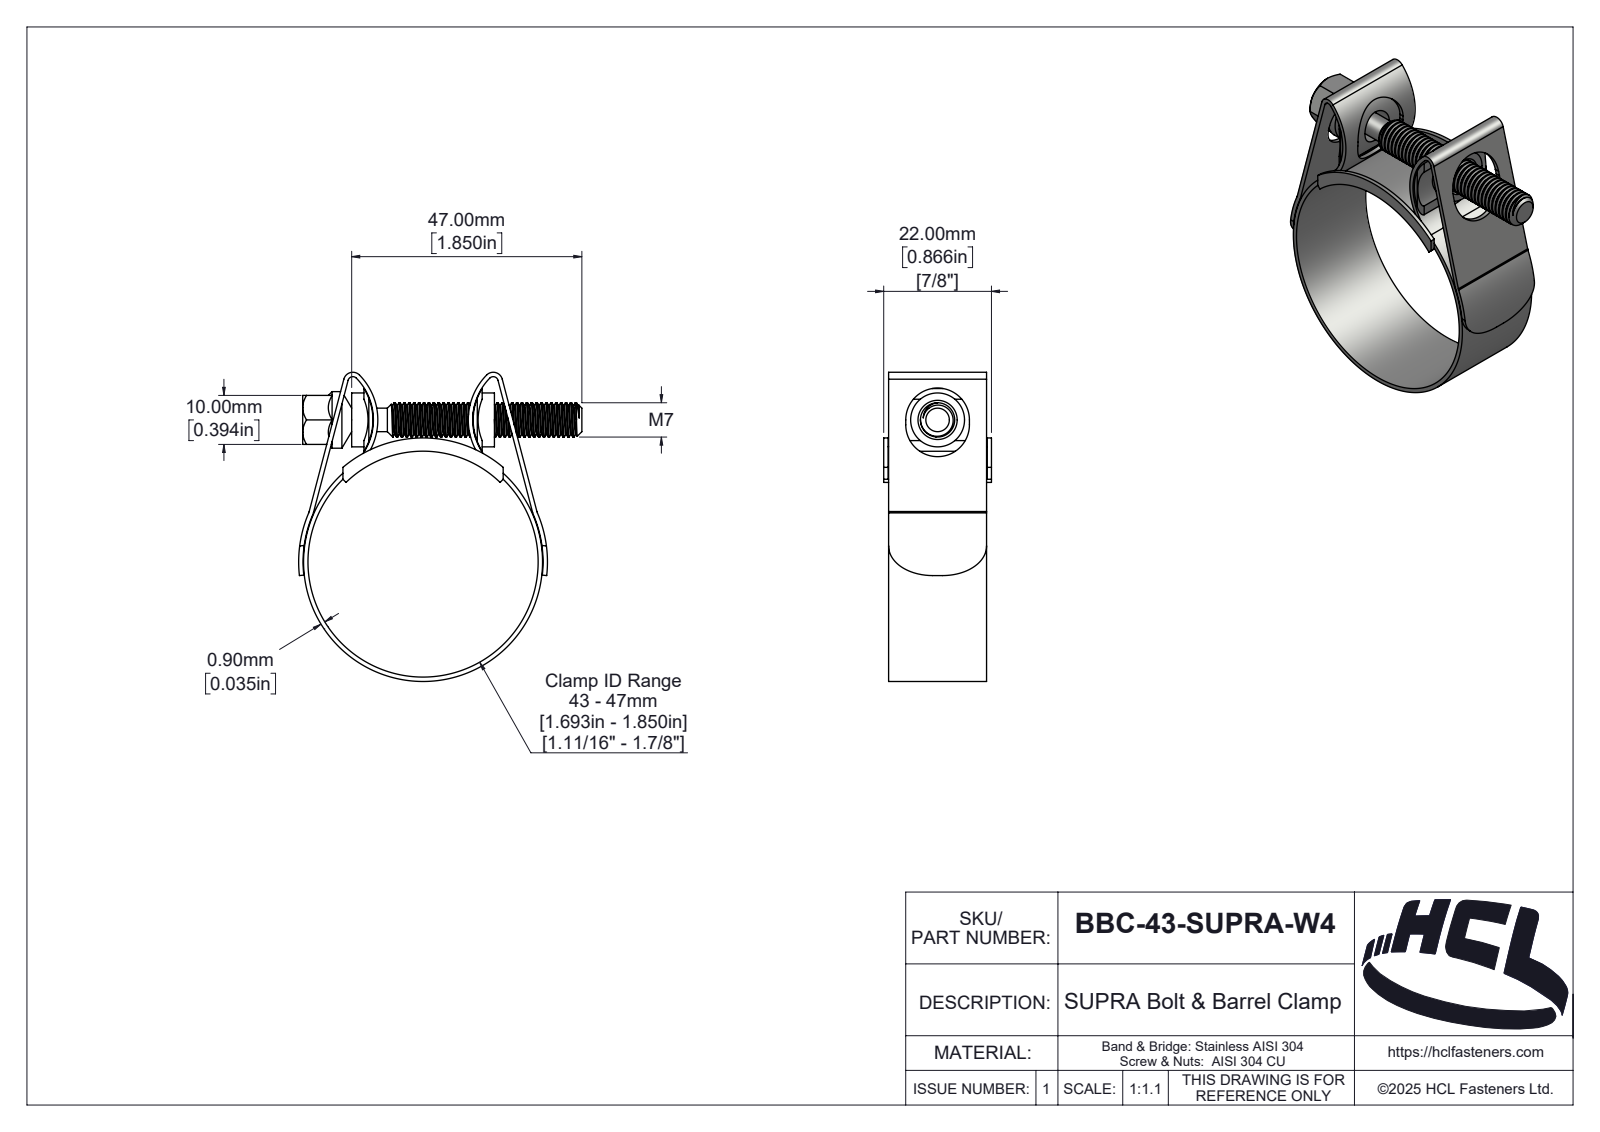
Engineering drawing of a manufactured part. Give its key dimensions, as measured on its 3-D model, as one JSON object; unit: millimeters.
{"part_name": "BBC-43-SUPRA-W4", "step_written_by": "SolidWorks 2025 (AUTOMOTIVE_DESIGN)", "units": "millimeters", "bodies": {"solids": 5, "faces": 314, "planar": 46, "cylindrical": 189, "other": 79}, "overall_size": [63.11, 57.83, 22], "volume_mm3": 7697, "surface_area_mm2": 14445, "round_holes": [[47, 1]], "round_bosses_or_shafts": [[11.55, 1], [11, 1], [7, 1], [4.8, 1]], "partial_cylinders_radius": [[1, 6], [1.9, 2], [2, 2], [2.9, 2], [6.5, 2], [11.07, 2], [12.07, 2], [12.17, 2]], "face_to_face_distances": [0.9, 20, 1, 21, 10, 21.1, 20.1, 22, 2.5, 26.64]}
